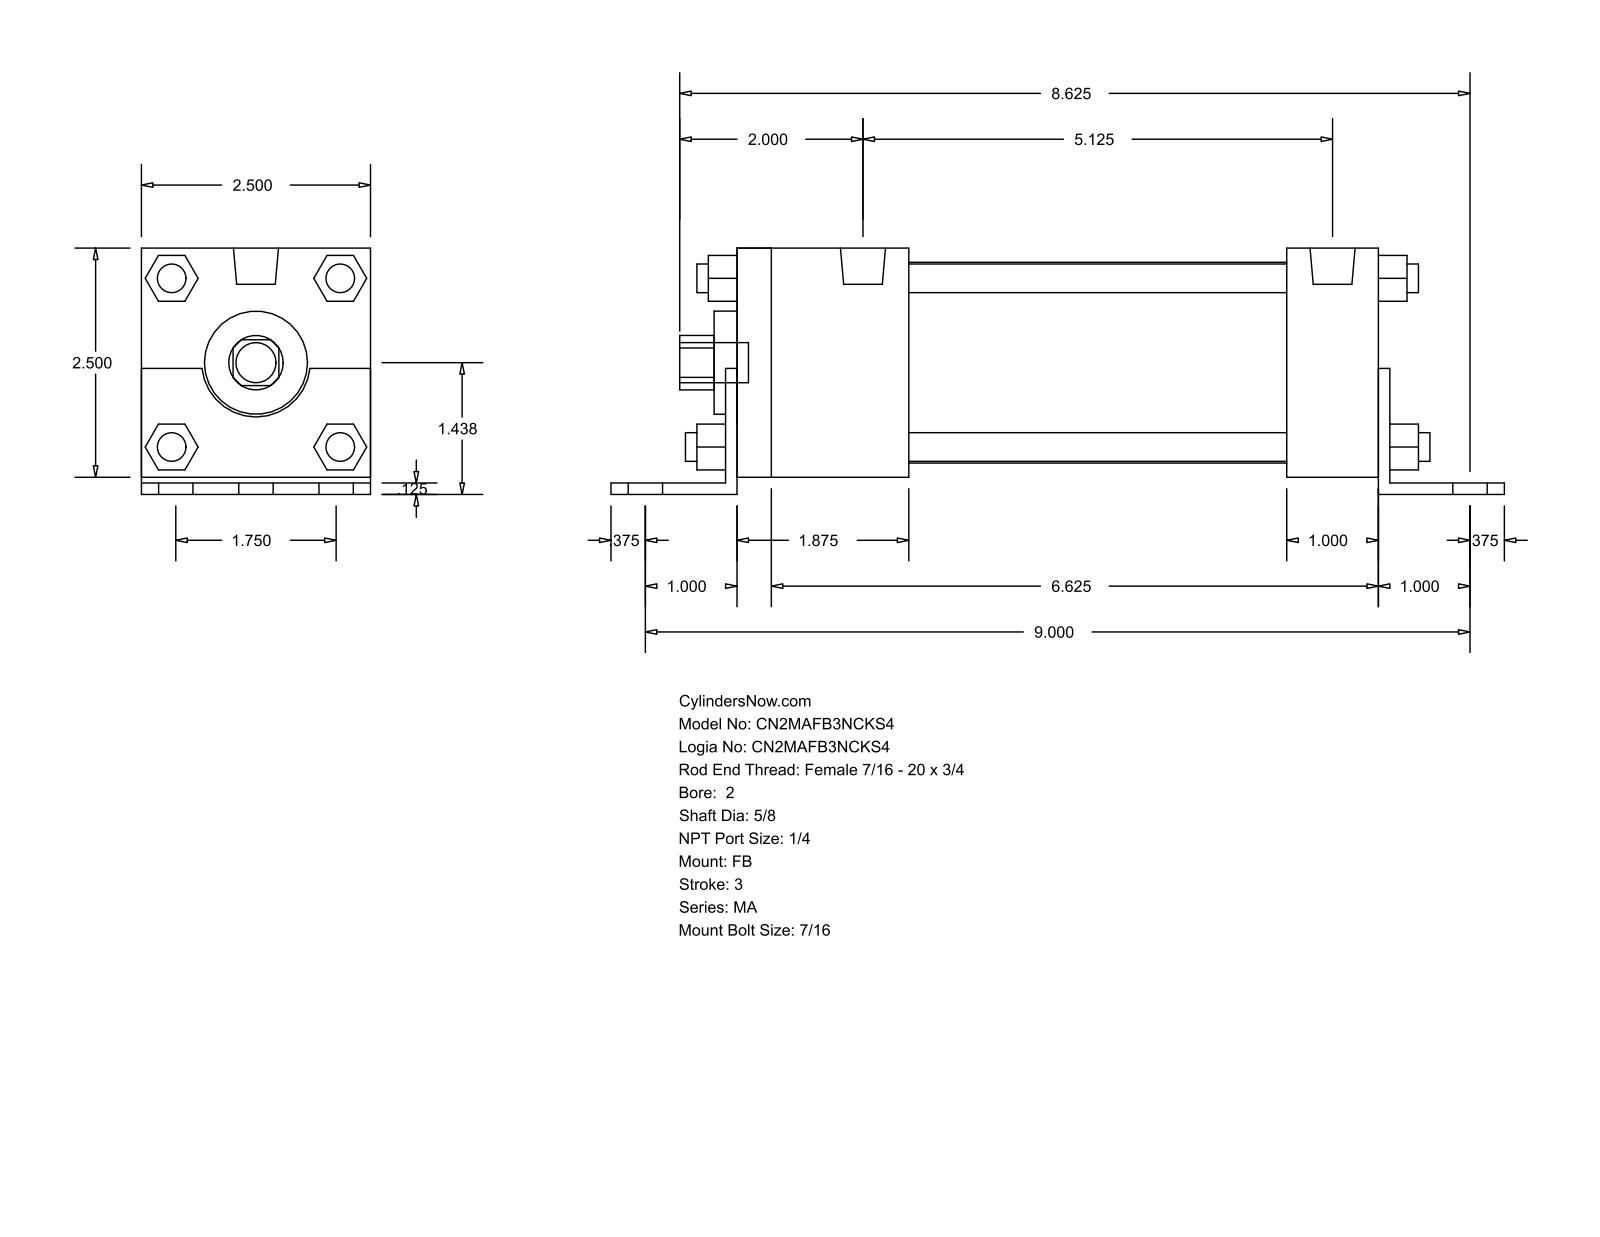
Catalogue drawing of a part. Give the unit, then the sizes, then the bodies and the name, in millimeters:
Units: millimetres
Overall size (bounding box): 247.65 × 68.26 × 63.5
Round holes (diameter × count): ⌀15.88 ×1, ⌀28.57 ×1, ⌀55.63 ×1
Round bosses / shafts (diameter × count): ⌀7.94 ×8, ⌀11.11 ×7, ⌀12.49 ×2
Partial cylindrical surfaces — rounded edges, fillets, slot ends (radius × count): R7.54 ×1, R15.05 ×1
Main face-to-face distances: 63.5, 3.17, 4.76, 68.26, 1.59, 65.09, 177.8, 184.15, 3.18, 180.97
Bodies: 0 solids, 140 faces (105 planar, 35 cylindrical, 0 other)
Part name (STEP PRODUCT): MA_FB__0200_0.625
STEP written by: GSSL Pune (CONFIG_CONTROL_DESIGN)
